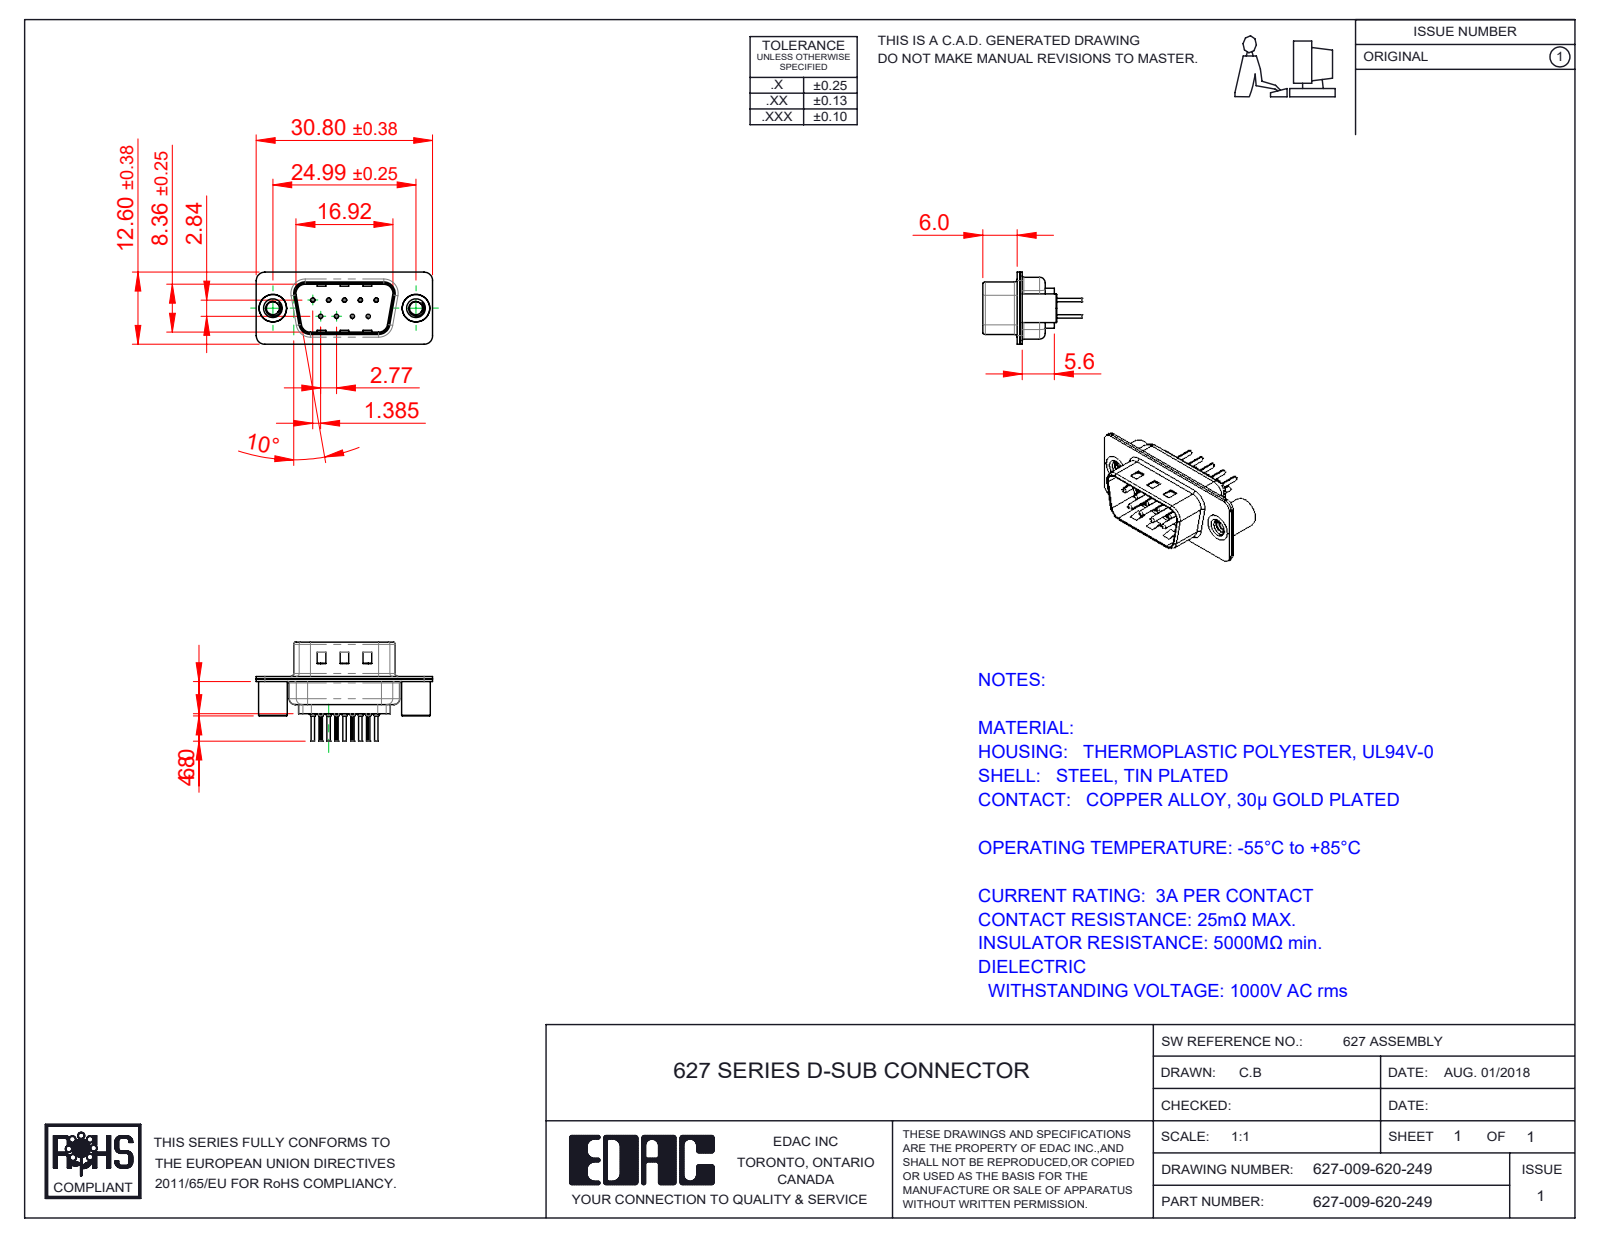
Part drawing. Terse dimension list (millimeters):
name: 627 Housing_09 LP; 627 4-40 Threaded Standoff BS; 627 Shell Front_09 Contacts; 627 Contact Row 2_20L (+3 more)
written by: SolidWorks 2020 (CONFIG_CONTROL_DESIGN)
unit: mm
bodies: 14 solids, 1208 faces (323 planar, 482 cylindrical, 403 other)
size: 30.8 × 17.3 × 12.6
volume: 1 408 mm³; area: 4 125 mm²
holes: 9× ⌀0.2, 9× ⌀0.35, 9× ⌀1.1, 9× ⌀1.6, 2× ⌀2.26, 2× ⌀4, 2× ⌀4.8
bosses: 9× ⌀2, 9× ⌀1.5, 9× ⌀0.75, 9× ⌀0.6, 2× ⌀5, 2× ⌀4.9
rounds: 18× R0.1, 18× R1.5, 12× R2, 8× R0.5, 8× R1.6, 4× R0.25, 4× R0.6, 4× R0.65
face distances: 0.45, 0.4, 0.9, 0.82, 9.58, 1.4, 8.76, 6.5, 0.5, 1.5
hole spacings: 3.16, 2.77, 5.54, 5.03, 5.04, 8.31, 7.48, 7.49
